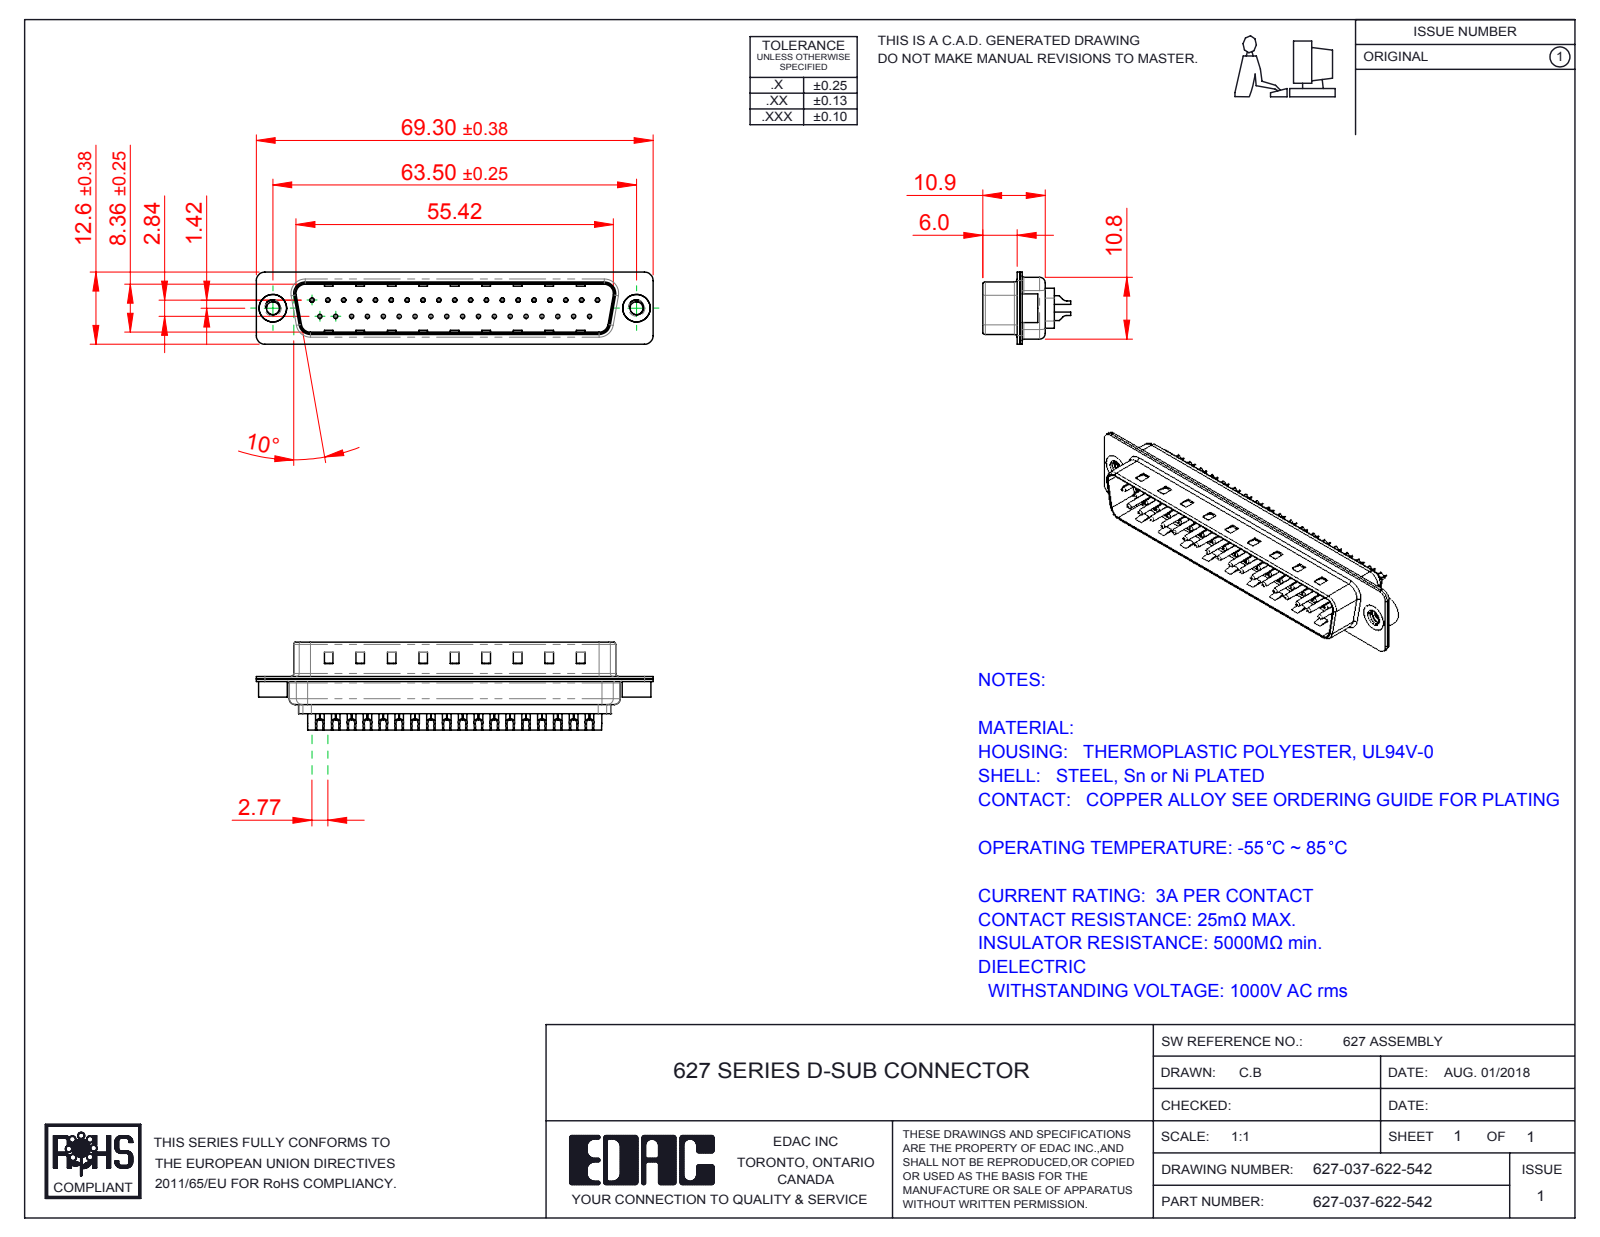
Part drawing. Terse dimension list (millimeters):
name: 627 4-40 Threaded Rivet; 627 Shell Rear_37 Contacts; 627 Housing_37 LP; 627 Shell Front_37 Contacts (+3 more)
written by: SolidWorks 2016 (CONFIG_CONTROL_DESIGN)
unit: mm
bodies: 42 solids, 2780 faces (721 planar, 1214 cylindrical, 845 other)
size: 69.3 × 15.35 × 12.6
volume: 3 717 mm³; area: 10 764 mm²
holes: 37× ⌀0.35, 37× ⌀1.1, 37× ⌀1.6, 2× ⌀2.26, 2× ⌀4, 2× ⌀4.8
bosses: 37× ⌀2, 37× ⌀1.5, 37× ⌀0.75, 2× ⌀5, 2× ⌀4.9
rounds: 16× R1.5, 12× R2, 8× R0.5, 8× R1.6, 6× R1, 4× R0.25, 4× R0.6, 4× R0.65
face distances: 0.4, 0.82, 9.58, 0.45, 8.76, 1.5, 0.9, 1.4, 6.05, 0.42
hole spacings: 3.16, 2.77, 5.54, 8.31, 5.04, 10.1, 11.08, 12.78
